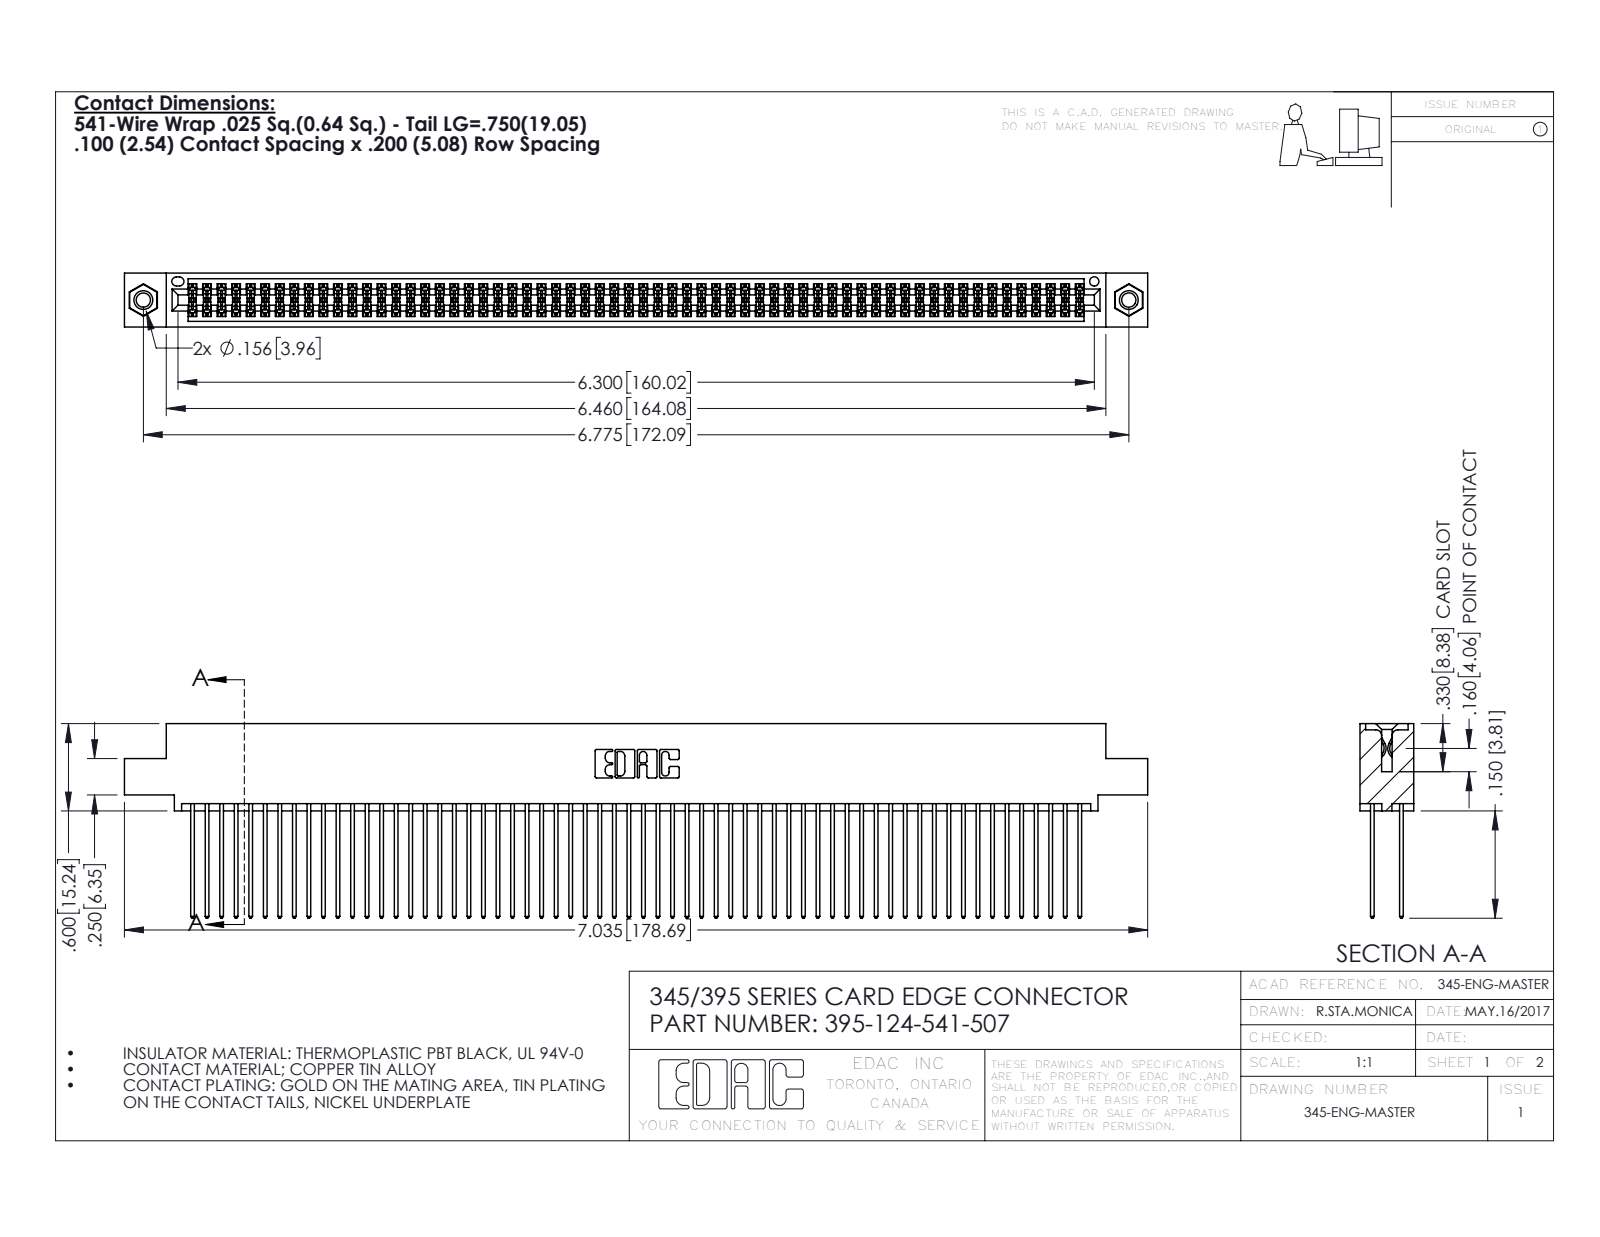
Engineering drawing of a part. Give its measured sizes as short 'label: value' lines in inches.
name: 345 Part_0.110 Offset - 0.156 Dia-TI; 345-292-001_345-293-141; 345-250-001_345-250-005-103; 395-124-541-507
written by: SolidWorks 2016 (CONFIG_CONTROL_DESIGN)
unit: in
bodies: 127 solids, 6390 faces (4208 planar, 2166 cylindrical, 16 other)
size: 7.035 × 1.337 × 0.37
volume: 1.109 in³; area: 47.6 in²
holes: 2× ⌀0.098, 2× ⌀0.125, 2× ⌀0.156, 1× ⌀0.064
bosses: 2× ⌀0.155
rounds: 186× R0.006, 124× R0.01, 22× R0.01, 6× R0.007, 6× R0.031, 3× R0.026, 2× R0.014, 2× R0.019
face distances: 0.072, 0.298, 0.2, 0.098, 0.272, 0.025, 0.225, 0.37, 0.175, 0.149
hole spacings: 0.27, 6.539, 6.775
